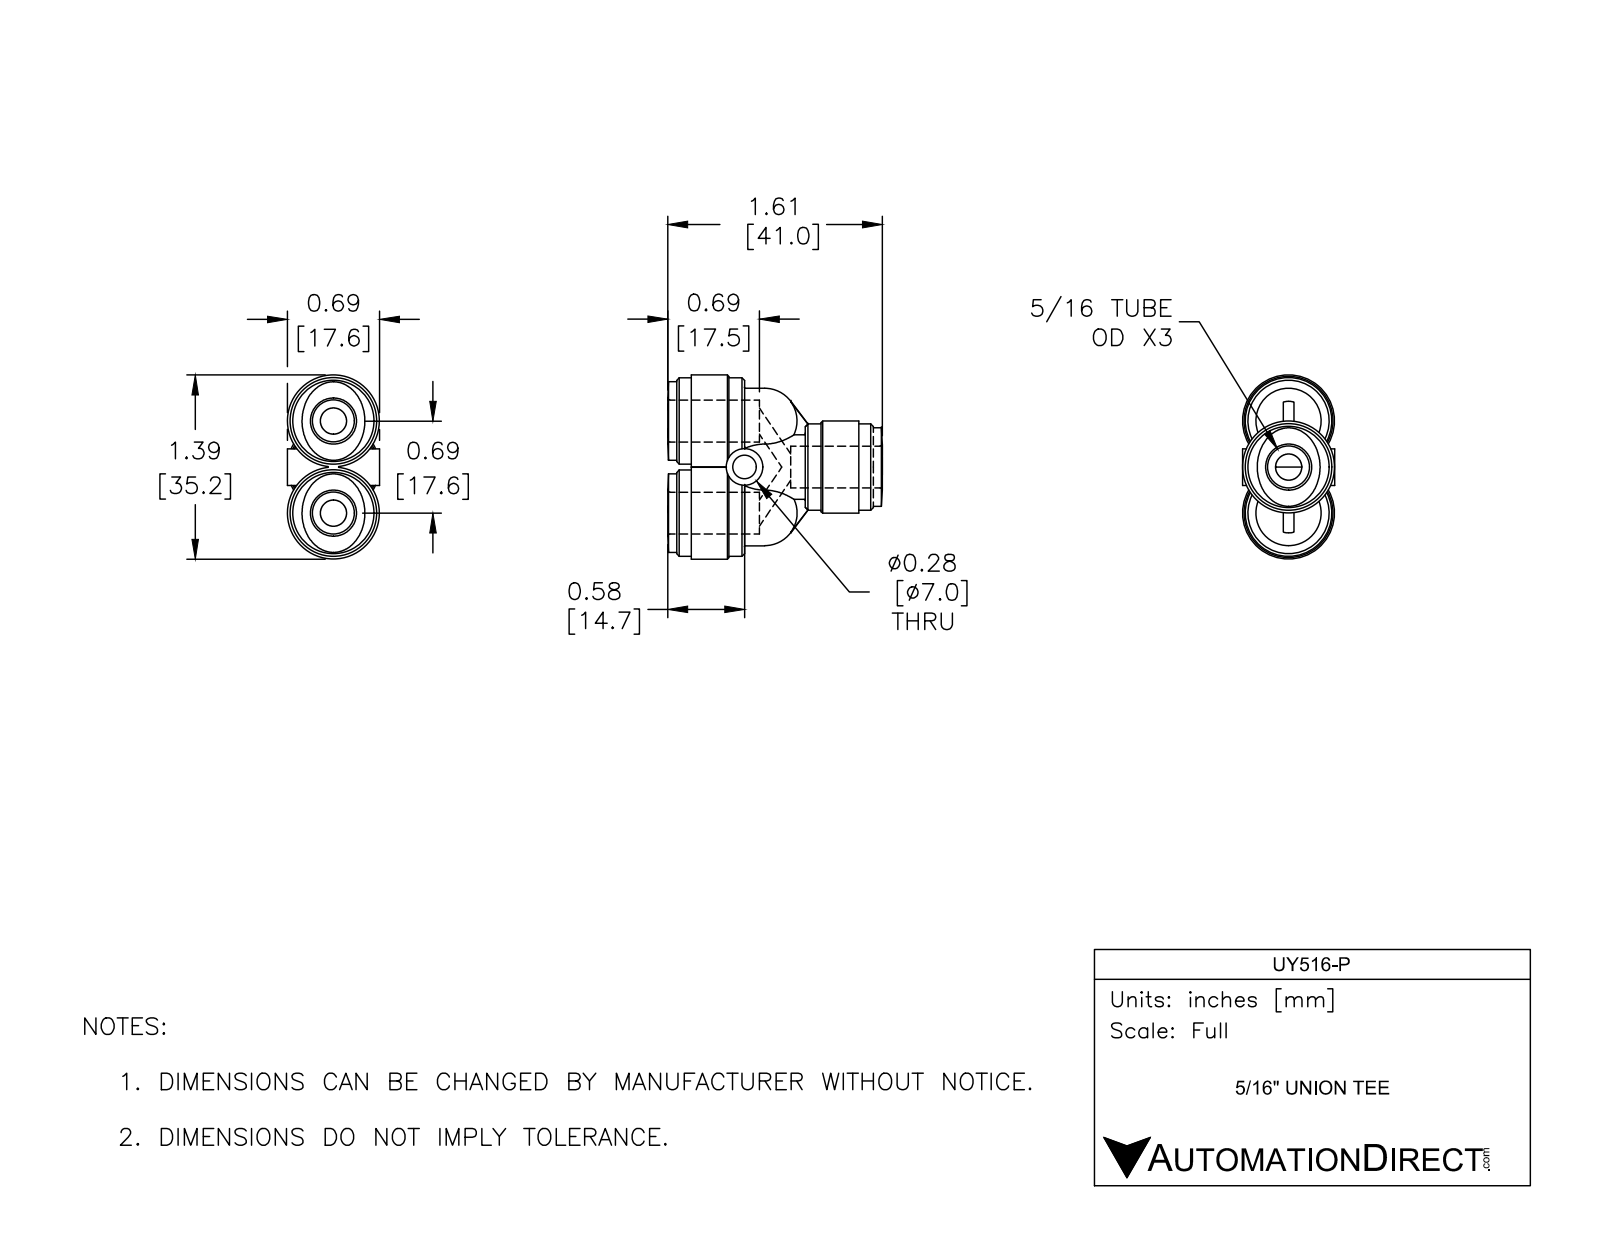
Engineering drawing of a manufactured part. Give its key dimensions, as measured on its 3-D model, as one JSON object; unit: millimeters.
{"part_name": "UY516-P", "step_written_by": "SolidWorks 2017 (AUTOMOTIVE_DESIGN)", "units": "millimeters", "bodies": {"solids": 1, "faces": 108, "planar": 23, "cylindrical": 34, "other": 51}, "overall_size": [41, 35.2, 17.6], "volume_mm3": 9880, "surface_area_mm2": 5914, "round_holes": [[8, 3], [4.5, 1]], "round_bosses_or_shafts": [[17.6, 3], [16.5, 3], [12.5, 3], [7, 1]], "face_to_face_distances": [13, 2.8, 21.8, 24.6, 15.8, 10.2, 8.8, 34.8, 19, 11.6], "hole_center_spacings": [8.8, 17.6]}
